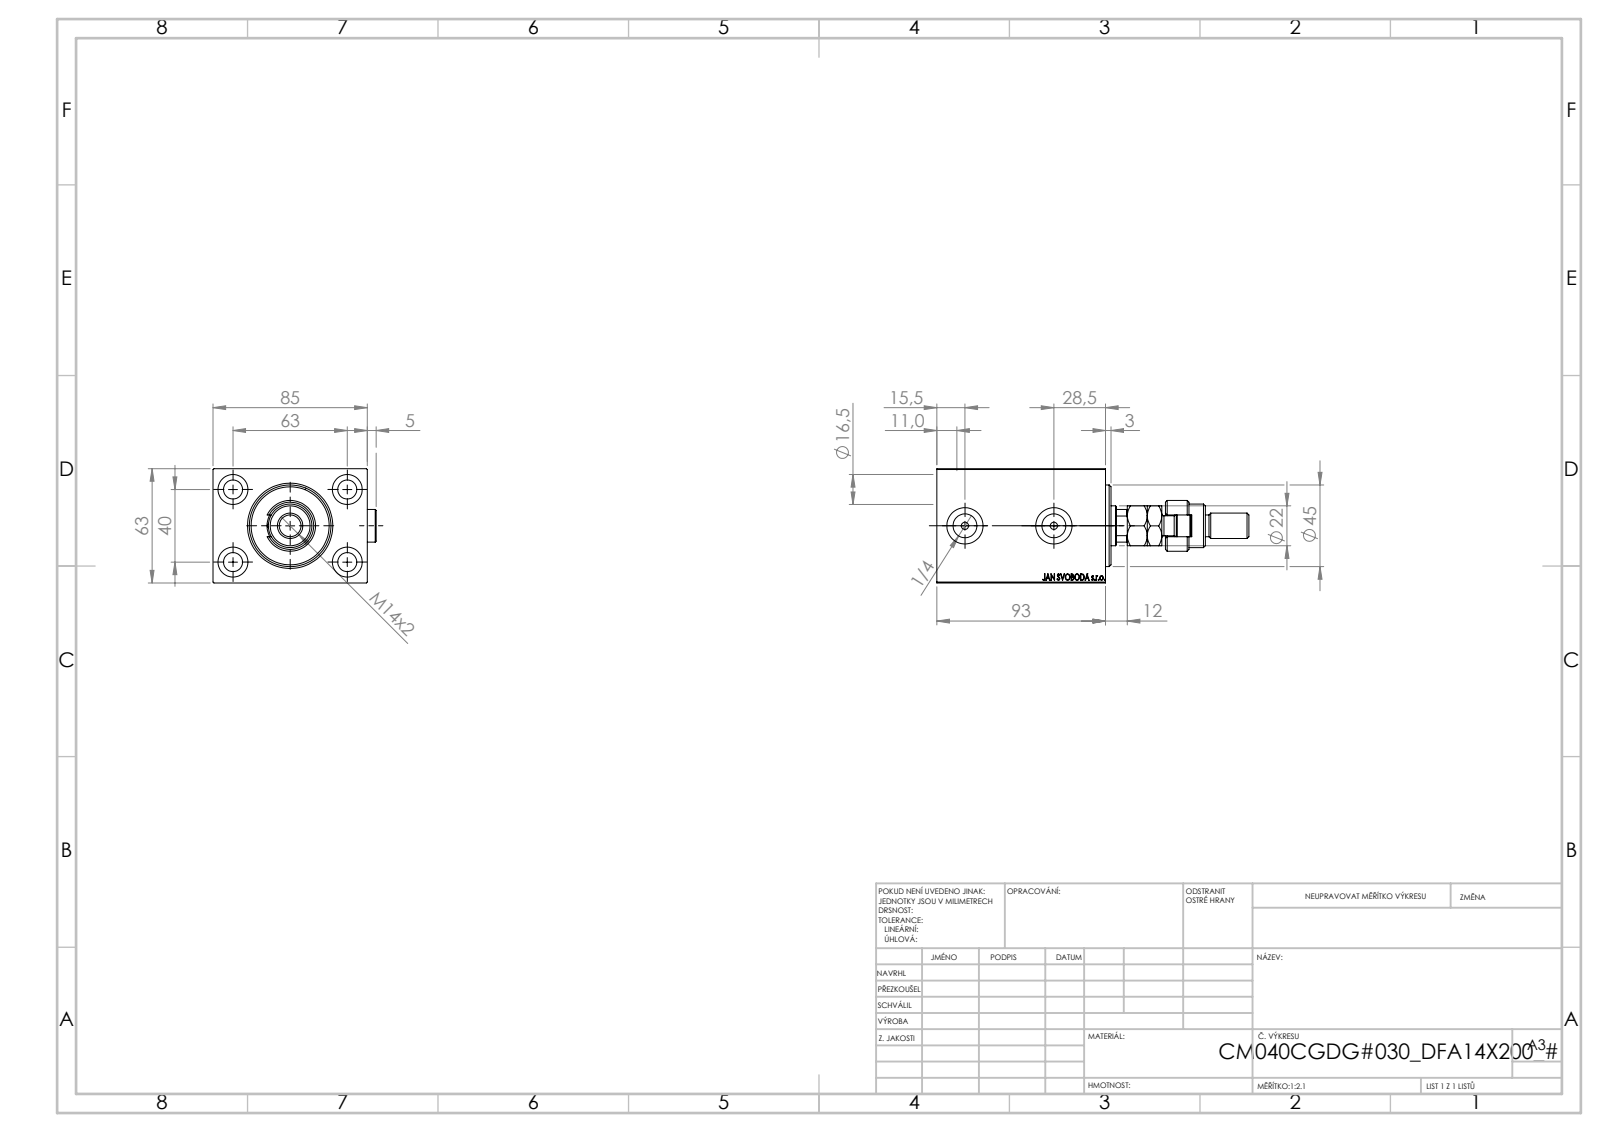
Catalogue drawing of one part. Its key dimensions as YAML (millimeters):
part_name: "V450CM_VC_B; Zatka_OIL_PORT; V450CM_C_VCP; FEMALE_PART_FOR_DFA (+2 more)"
step_written_by: "SolidWorks 2019 (CONFIG_CONTROL_DESIGN)"
units: millimeters
bodies: {solids: 7, faces: 1001, planar: 470, cylindrical: 89, other: 442}
overall_size: [172, 89.9, 63]
volume: 449701
surface_area: 91207
round_holes:
  - {diameter: 10.5, count: 4}
  - {diameter: 16.5, count: 4}
  - {diameter: 4, count: 2}
  - {diameter: 13.16, count: 2}
  - {diameter: 20, count: 2}
  - {diameter: 12.5, count: 1}
  - {diameter: 22, count: 1}
  - {diameter: 25.5, count: 1}
  - {diameter: 40, count: 1}
  - {diameter: 42, count: 1}
  - {diameter: 45, count: 1}
round_bosses_or_shafts:
  - {diameter: 18, count: 3}
  - {diameter: 28, count: 1}
  - {diameter: 24, count: 1}
  - {diameter: 14, count: 1}
  - {diameter: 12, count: 1}
  - {diameter: 11, count: 1}
partial_cylinders:
  - {radius: 9.75, count: 1}
  - {radius: 10.5, count: 1}
face_to_face_distances: [63, 85, 12, 81, 93, 84.9, 3, 30, 45, 15]
hole_center_spacings: [37.31, 40, 63, 74.63, 49]
